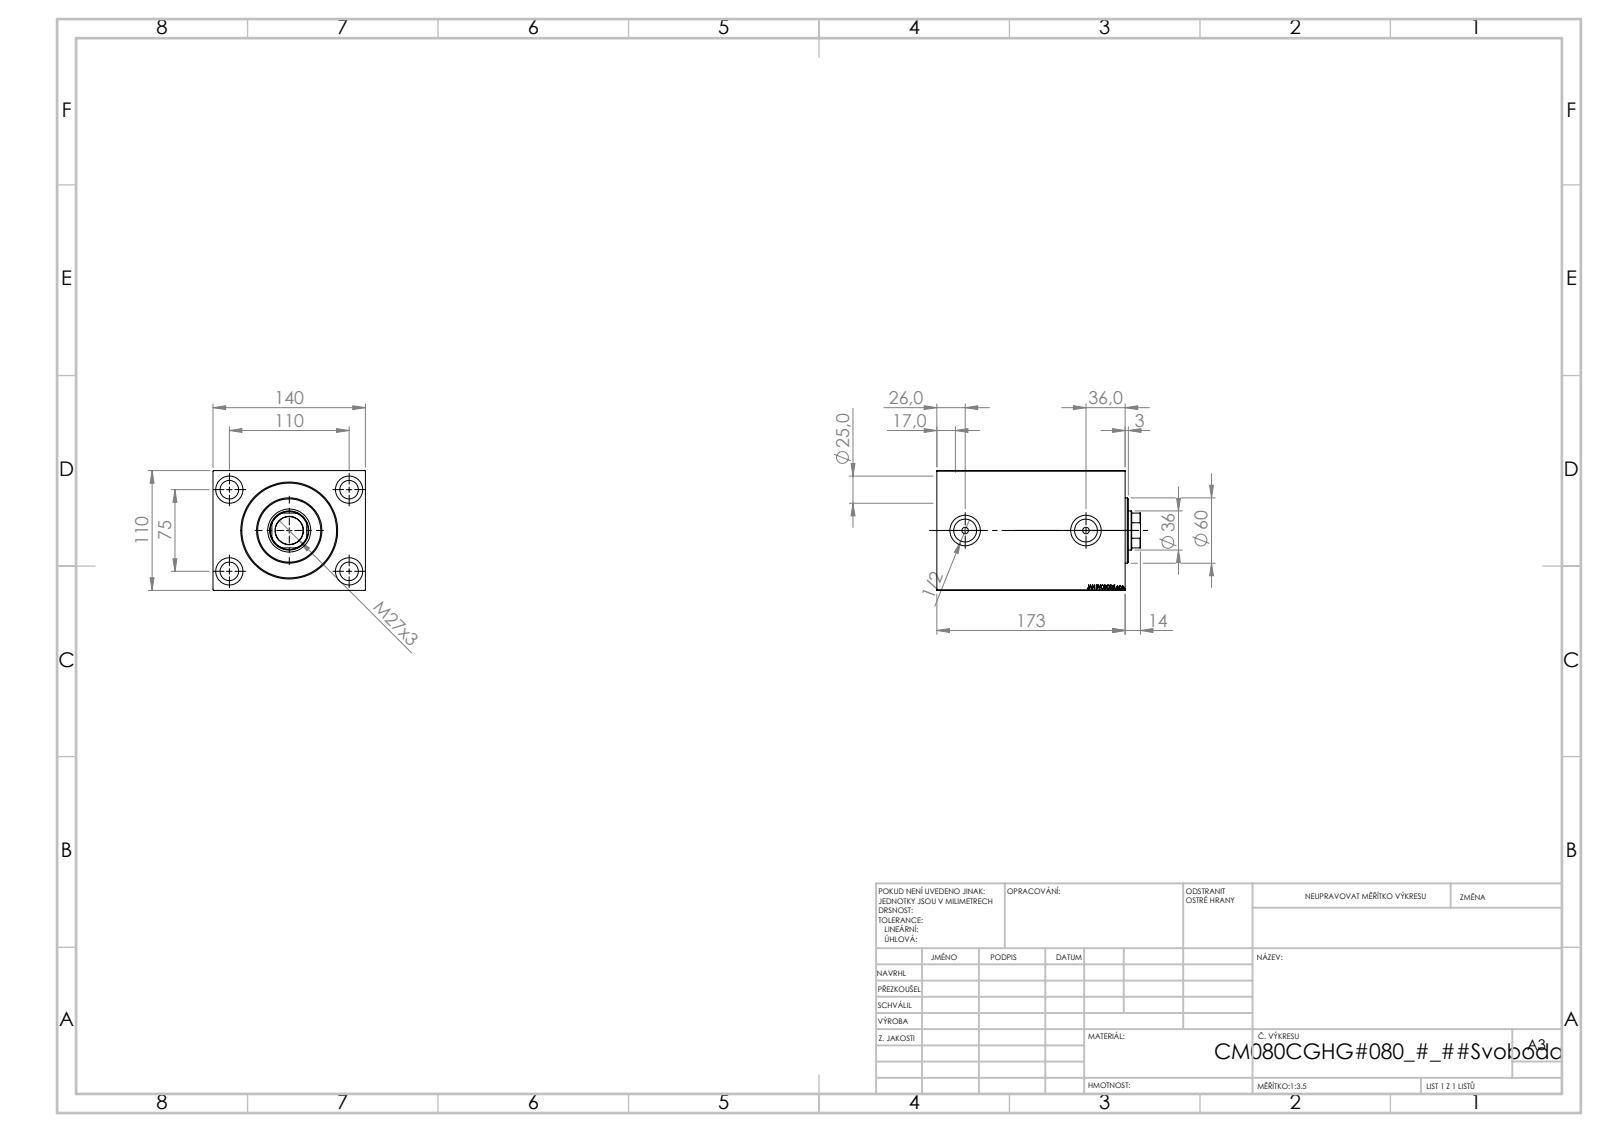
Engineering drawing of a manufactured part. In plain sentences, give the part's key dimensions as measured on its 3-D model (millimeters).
The part is named "V450CM_C_Body; V450CM_VC_B; V450CM_C_VCP". Its 3-D file was written by "SolidWorks 2019 (CONFIG_CONTROL_DESIGN)". It is 3 solids with 865 faces: 409 planar, 62 cylindrical and 394 other. Overall it measures 187 by 140 by 110 millimeters. Its volume is 2 141 000 cubic millimeters and its surface area 251 592 square millimeters. Round holes: 4 of diameter 17, 4 of diameter 25, 2 of diameter 6, 2 of diameter 20.96, 2 of diameter 28, 1 of diameter 25.5, 1 of diameter 36, 1 of diameter 39.5, 1 of diameter 80, 1 of diameter 82, 1 of diameter 87. Round bosses or shafts: 1 of diameter 60. Partial cylindrical surfaces (rounded edges, fillets, slot ends): 1 of radius 17.5. The main face-to-face distances are 110, 140, 173, 152, 21, 159, 14, 138, 94, 80. The hole center spacings are 66.57, 75, 110, 133.14, 111.
